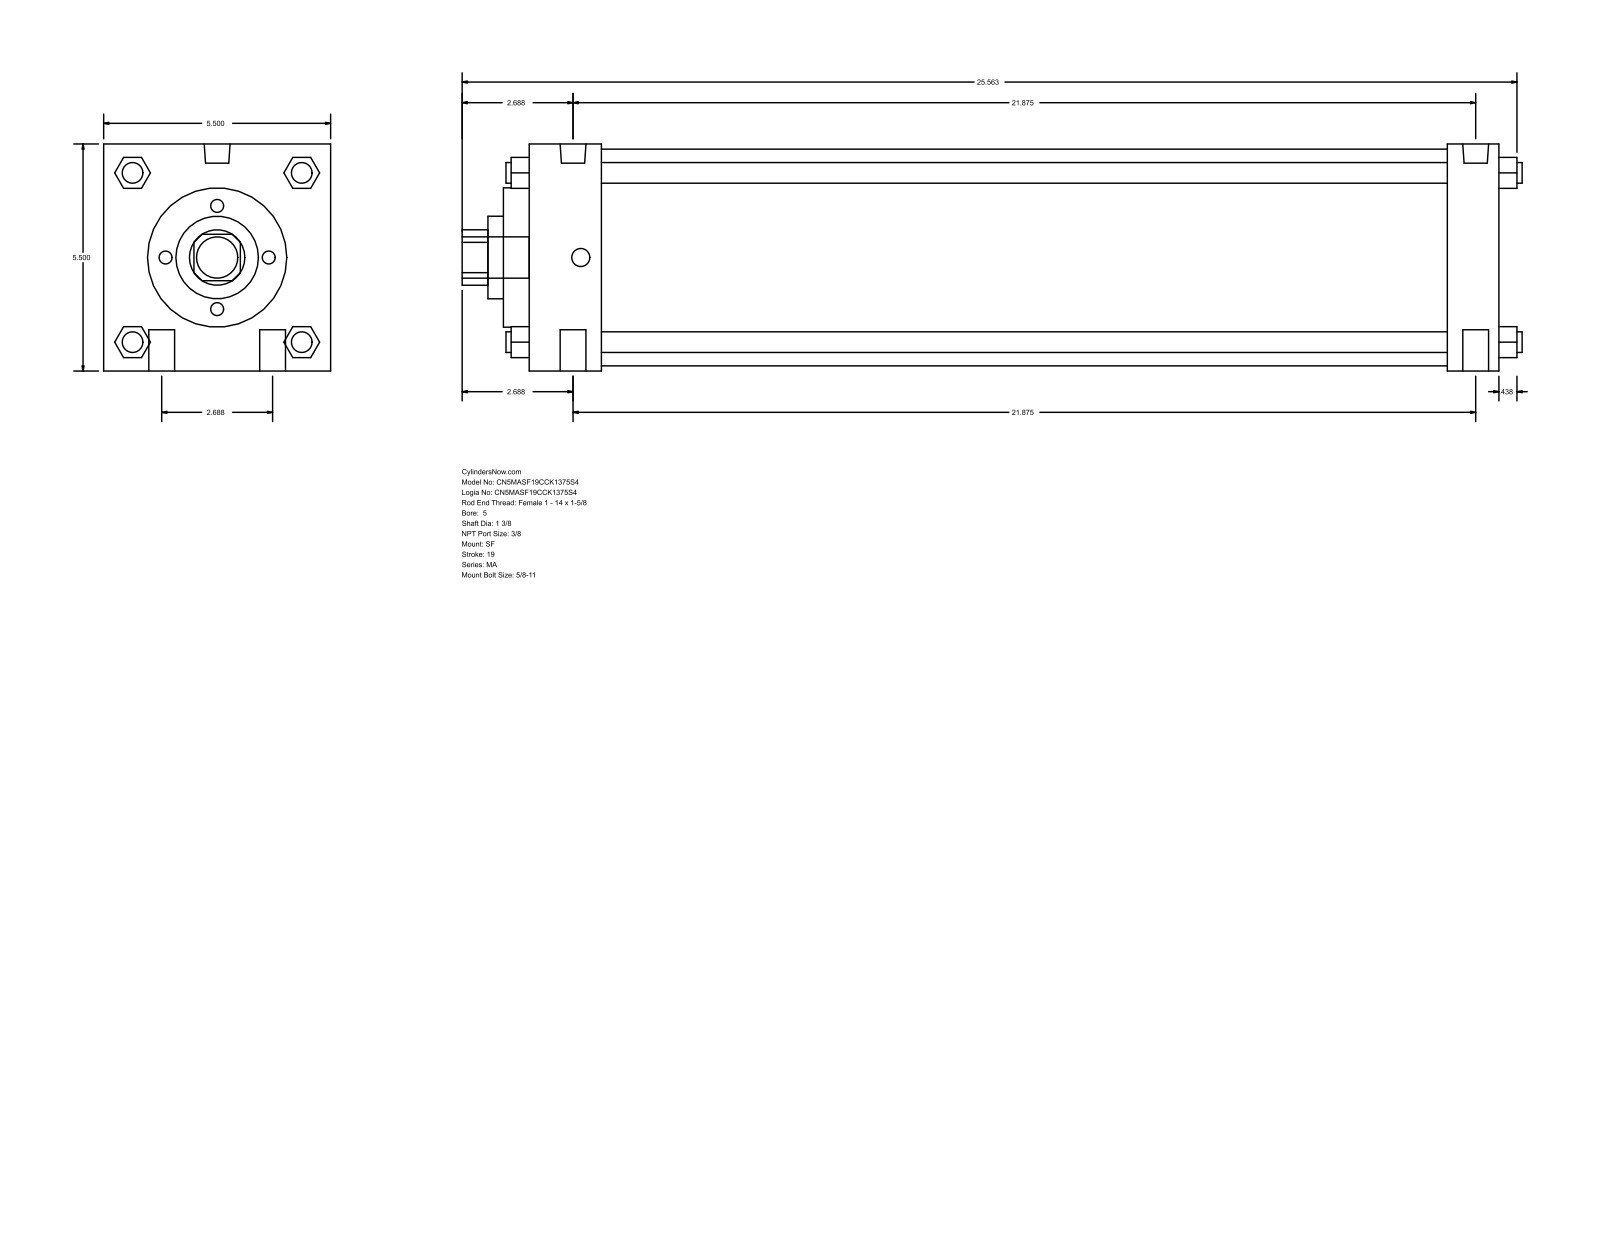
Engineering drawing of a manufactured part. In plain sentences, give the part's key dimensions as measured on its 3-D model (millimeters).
The part is named "MA_SF__0500_1.375". Its 3-D file was written by "GSSL Pune (CONFIG_CONTROL_DESIGN)". It is 0 solids with 126 faces: 95 planar, 31 cylindrical and 0 other. Overall it measures 652.46 by 139.7 by 139.7 millimeters. Round holes: 1 of diameter 34.92, 1 of diameter 50.8, 1 of diameter 85.72, 1 of diameter 133.35. Round bosses or shafts: 4 of diameter 15.88, 4 of diameter 12.7, 2 of diameter 15.93, 2 of diameter 11.11, 1 of diameter 25.4. Partial cylindrical surfaces (rounded edges, fillets, slot ends): 1 of radius 17.06. The main face-to-face distances are 139.7, 596.9, 44.45, 565.15, 520.7, 552.45, 31.75, 15.87, 60.32, 581.02.
